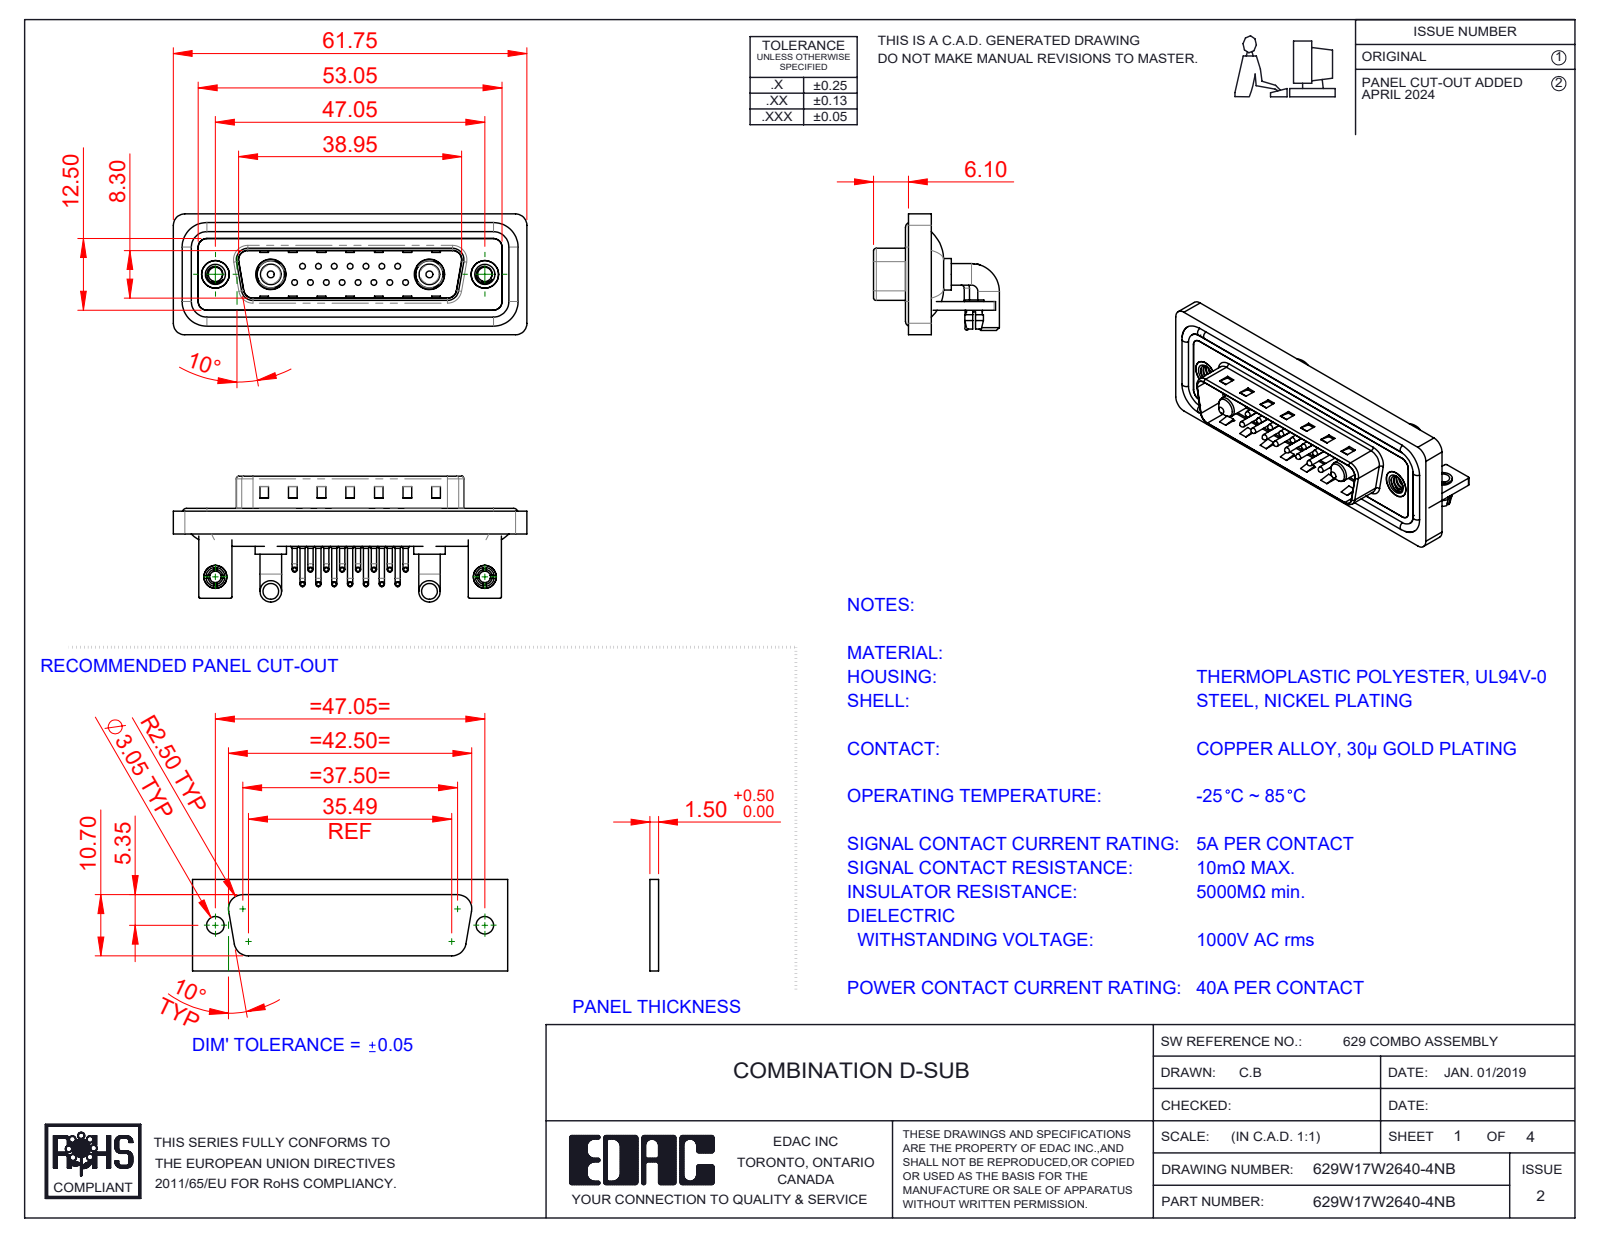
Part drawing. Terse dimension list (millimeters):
name: 629Combo Board Lock; Power Pin_40A RA; 629Combo Contact Row 2; 629Combo Waterproof Housing_25 Contacts (+7 more)
written by: SolidWorks 2023 (CONFIG_CONTROL_DESIGN)
unit: mm
bodies: 30 solids, 2349 faces (1257 planar, 820 cylindrical, 272 other)
size: 61.75 × 21.98 × 21.1
volume: 7 966 mm³; area: 13 487 mm²
holes: 17× ⌀2, 15× ⌀0.75, 15× ⌀1.6, 4× ⌀2.5, 2× ⌀3.2, 2× ⌀4, 2× ⌀4.8, 2× ⌀4.85, 2× ⌀5, 2× ⌀5.3
bosses: 30× ⌀0.9, 15× ⌀1.5, 15× ⌀1, 15× ⌀0.65, 4× ⌀3.75, 4× ⌀1.6, 2× ⌀5.5, 2× ⌀5.2
rounds: 19× R2, 18× R1.5, 16× R0.25, 15× R1.01, 9× R0.5, 8× R1.6, 4× R0.6, 4× R0.65
face distances: 0.4, 0.8, 2.1, 1.5, 2.9, 1.1, 4.1, 1.6, 4.5, 3.7
hole spacings: 3.16, 2.77, 5.54, 8.31, 5.04, 7.49, 11.08, 5.03
